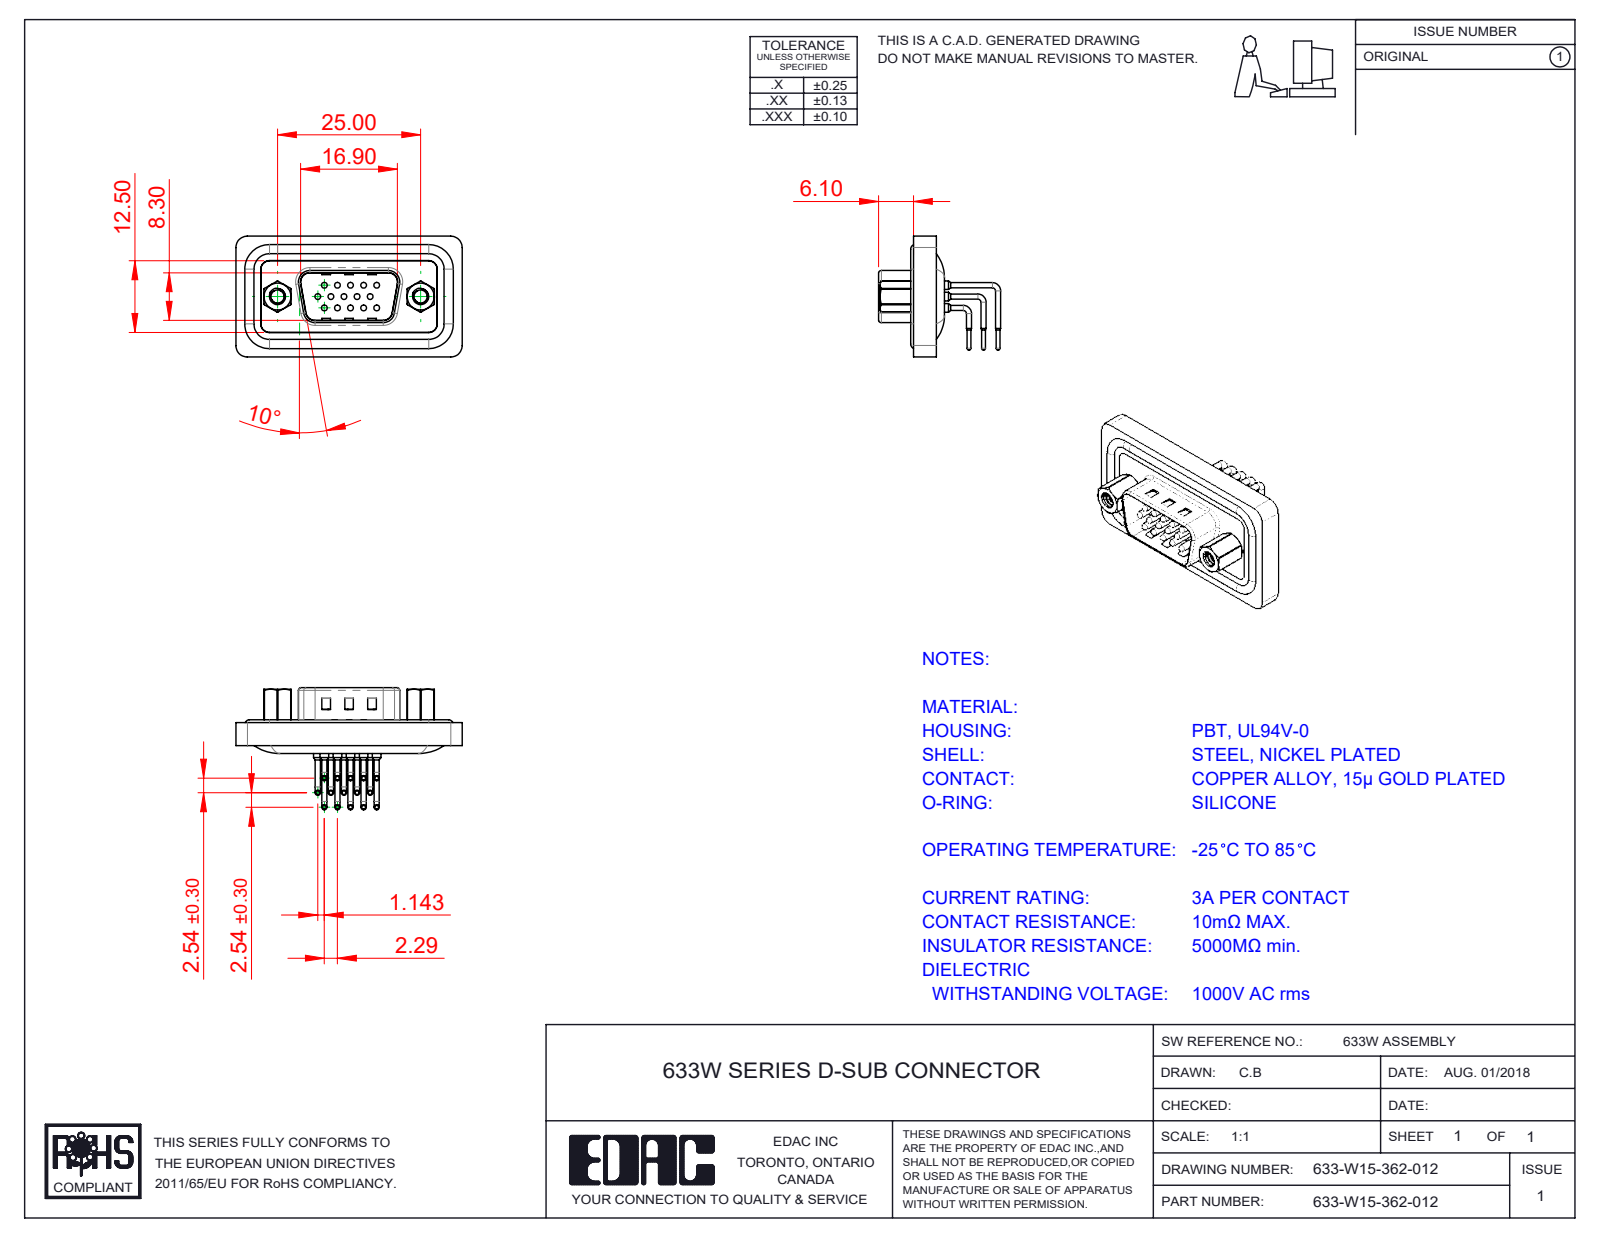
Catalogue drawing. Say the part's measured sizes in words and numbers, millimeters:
The part is named "633W 4-40 Hex Standoff; 633W Contact Row 2; 633W Contact Row 3; 633W Contact Row 1 (+5 more)". Its 3-D file was written by "SolidWorks 2016 (CONFIG_CONTROL_DESIGN)". It is 23 solids with 2118 faces: 1101 planar, 772 cylindrical and 245 other. Overall it measures 39.51 by 21.32 by 21.1 millimeters. Its volume is 4 080 cubic millimeters and its surface area 7 322 square millimeters. Round holes: 15 of diameter 1, 15 of diameter 1.5, 15 of diameter 1.7, 15 of diameter 2, 2 of diameter 2.26, 2 of diameter 2.29, 2 of diameter 4, 2 of diameter 4.8, 2 of diameter 5. Round bosses or shafts: 30 of diameter 0.9, 15 of diameter 0.65, 8 of diameter 1.5, 4 of diameter 1.6, 2 of diameter 4.9, 2 of diameter 2.79, 1 of diameter 5. Partial cylindrical surfaces (rounded edges, fillets, slot ends): 15 of radius 1.01, 14 of radius 1.5, 14 of radius 2, 8 of radius 0.5, 6 of radius 2.7, 4 of radius 0.9, 4 of radius 1.6, 4 of radius 4.3. The main face-to-face distances are 0.4, 2.9, 1.1, 1.6, 2.5, 4, 3.6, 1.8, 0.5, 0.7. The hole center spacings are 3.96, 2.28, 4.57, 2.29, 6.05, 6.04, 7.92, 6.86.
